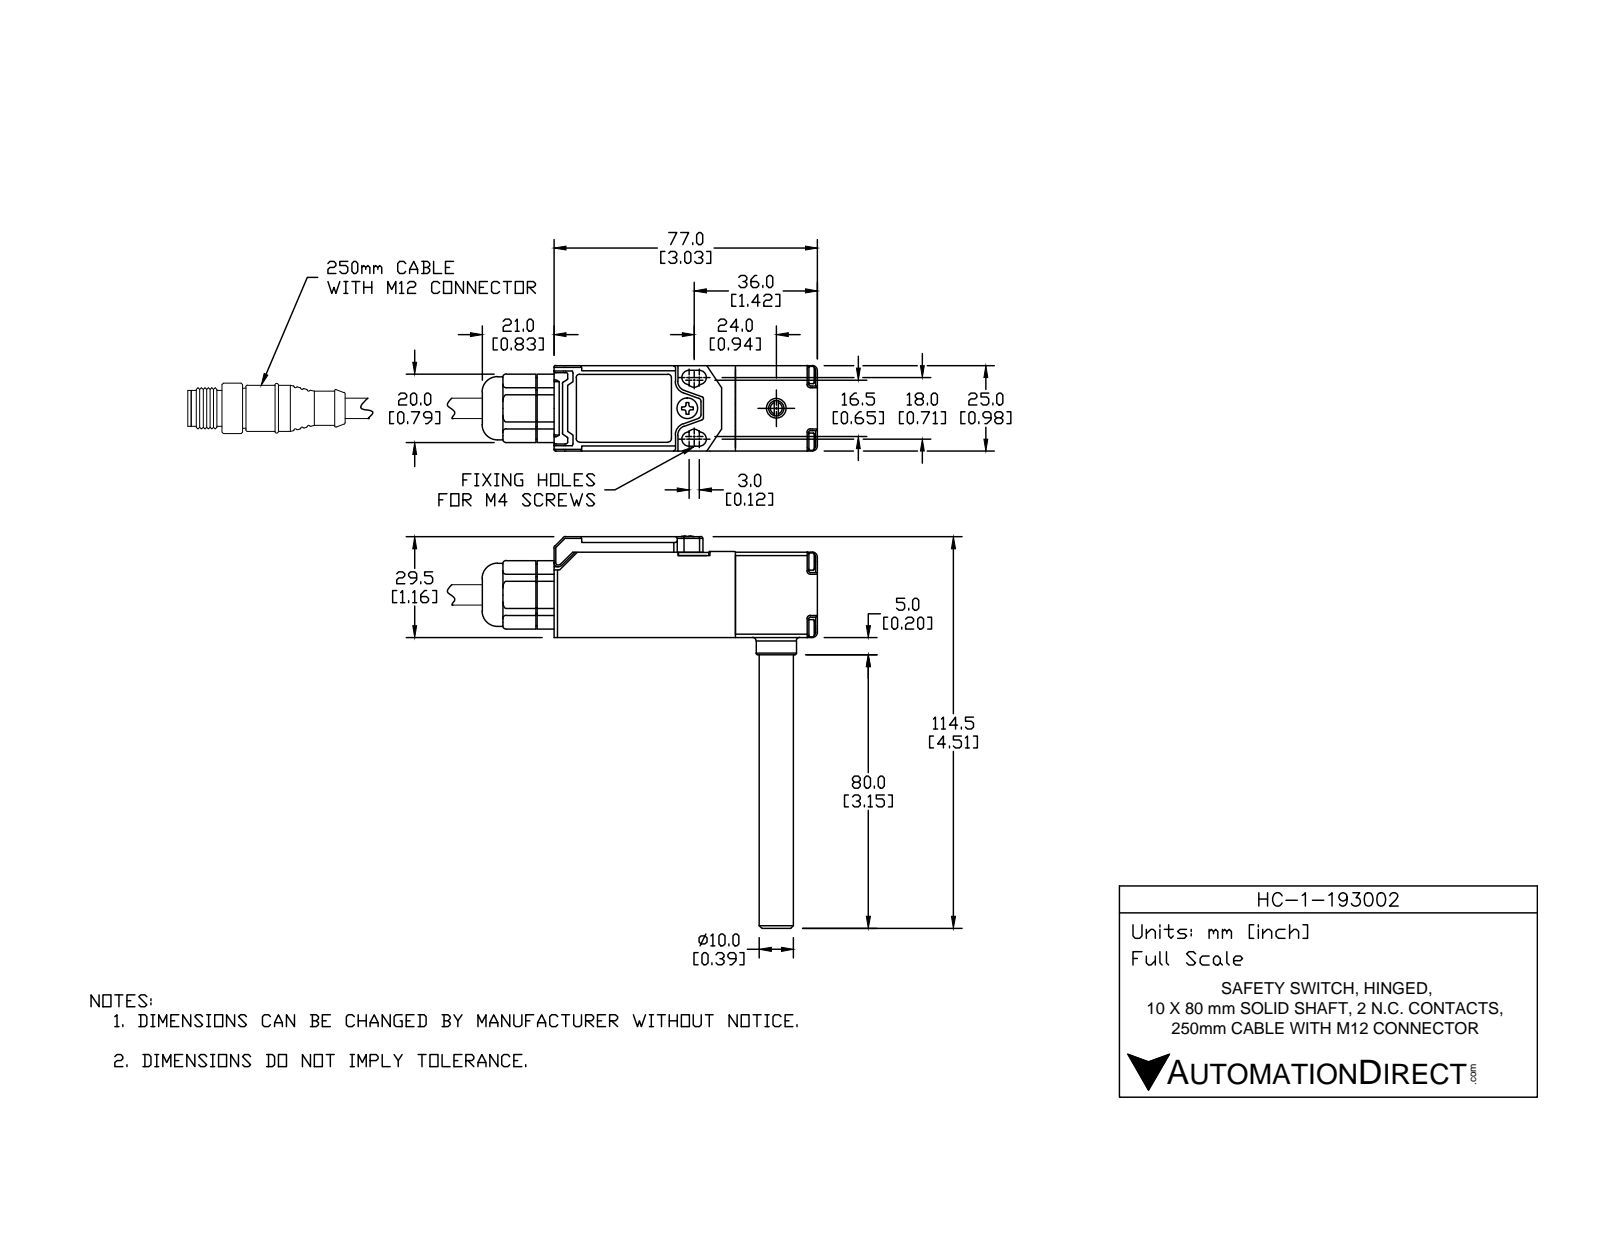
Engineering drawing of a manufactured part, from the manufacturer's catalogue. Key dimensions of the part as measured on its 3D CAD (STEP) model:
Part name (STEP PRODUCT): HC-1-193002
STEP written by: SolidWorks 2014 (AUTOMOTIVE_DESIGN)
Units: inches
Bodies: 14 solids, 1702 faces (700 planar, 601 cylindrical, 401 other)
Overall size (bounding box): 4.517 × 3.169 × 0.984
Volume: 1.932 in³ · Surface area: 44.5 in²
Round holes (diameter × count): ⌀0.126 ×5, ⌀0.094 ×4, ⌀0.059 ×2, ⌀0.063 ×2, ⌀0.071 ×2, ⌀0.087 ×2, ⌀0.142 ×2, ⌀0.055 ×1, ⌀0.081 ×1, ⌀0.098 ×1, ⌀0.102 ×1, ⌀0.185 ×1
Round bosses / shafts (diameter × count): ⌀0.102 ×5, ⌀0.197 ×4, ⌀0.079 ×4, ⌀0.138 ×2, ⌀0.74 ×1, ⌀0.531 ×1, ⌀0.394 ×1, ⌀0.386 ×1
Partial cylindrical surfaces — rounded edges, fillets, slot ends (radius × count): R0.02 ×226, R0.004 ×24, R0.012 ×20, R0.039 ×20, R0.059 ×7, R0.083 ×6, R0.11 ×6, R0.008 ×4
Main face-to-face distances: 0.984, 0.079, 0.071, 0.913, 0.039, 0.906, 0.945, 0.827, 0.874, 1.15
Hole centre spacings: 0.543, 0.768, 0.171, 0.187, 0.245, 0.414, 0.423, 0.426
